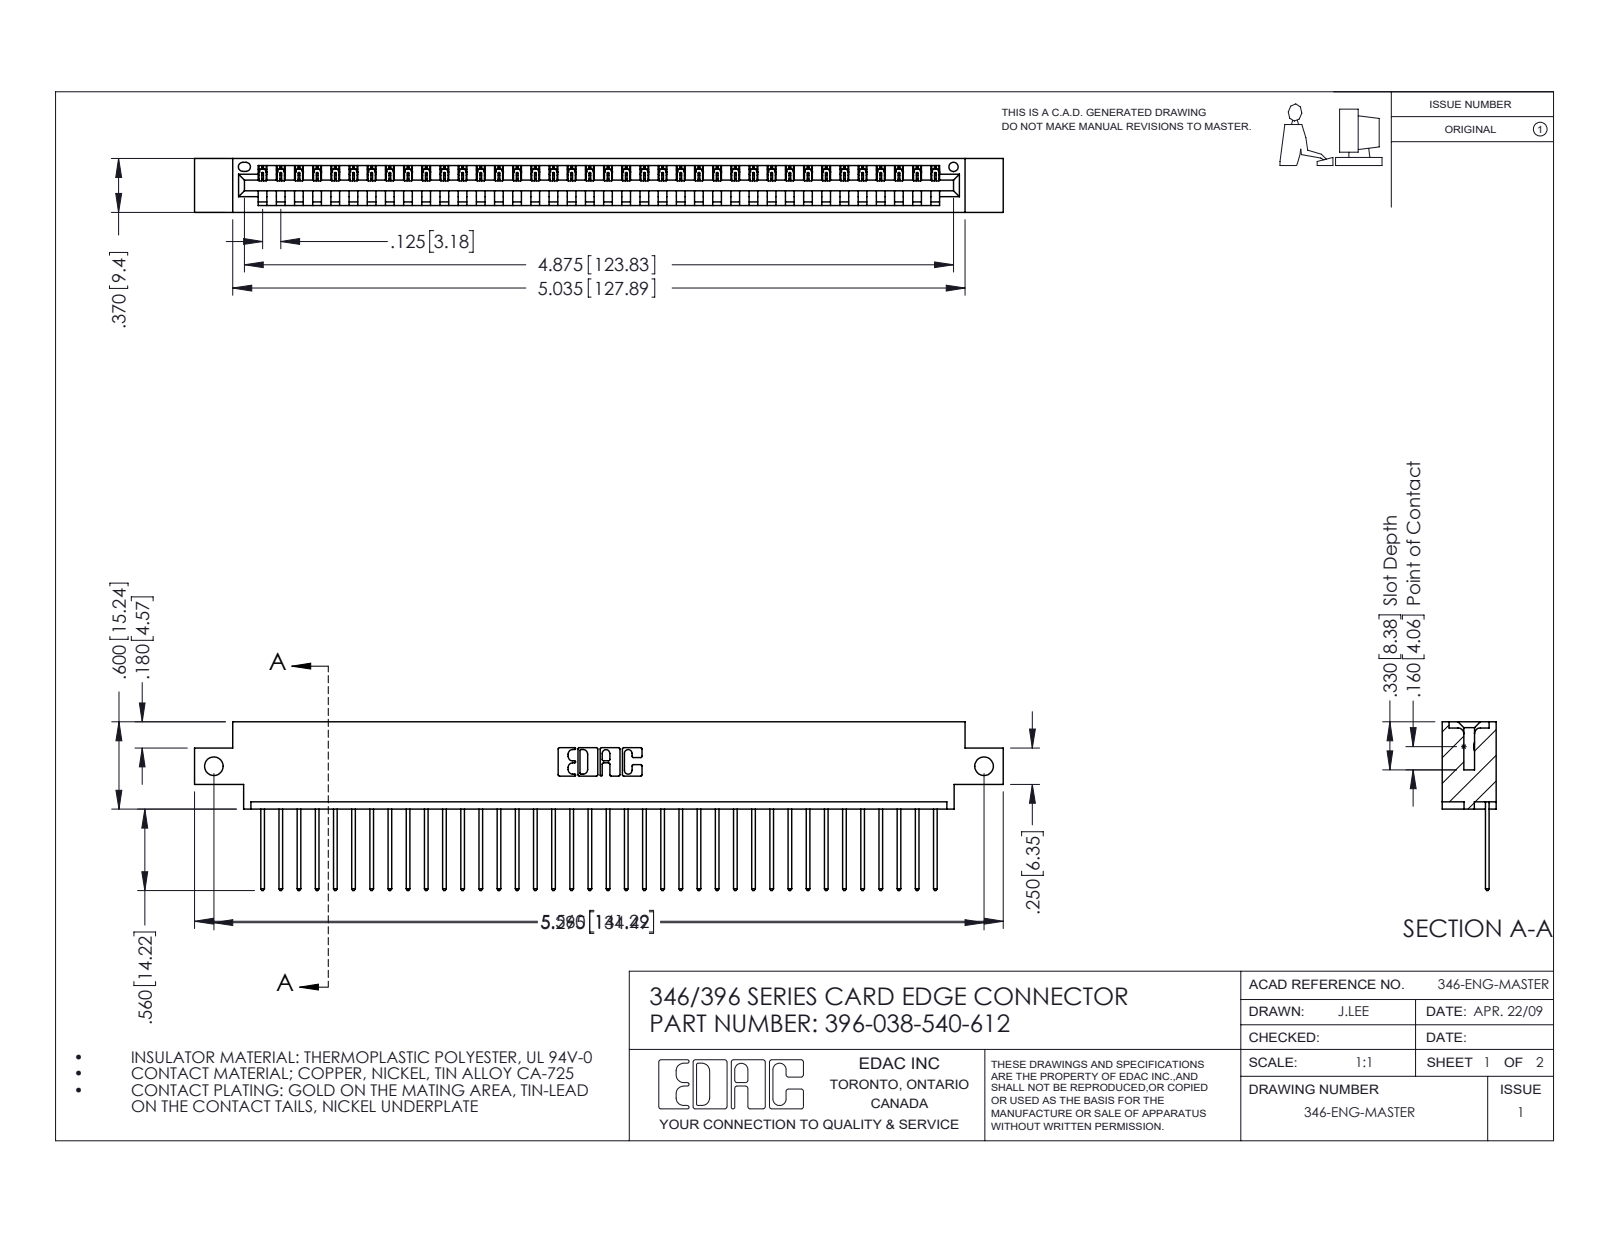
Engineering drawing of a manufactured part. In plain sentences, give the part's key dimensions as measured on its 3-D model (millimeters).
The part is named "396-038-540-612; 346 Part_0.170 Offset - Side Mount; 345-292-001_345-293-140". Its 3-D file was written by "SolidWorks 2016 (CONFIG_CONTROL_DESIGN)". It is 39 solids with 2330 faces: 1600 planar, 730 cylindrical and 0 other. Overall it measures 141.2 by 29.5 by 9.4 millimeters. Its volume is 13 300 cubic millimeters and its surface area 16 970 square millimeters. Round holes: 2 of diameter 3.3, 1 of diameter 1.6. Partial cylindrical surfaces (rounded edges, fillets, slot ends): 76 of radius 0.2, 76 of radius 0.3, 22 of radius 0.3, 6 of radius 0.2, 6 of radius 0.8, 3 of radius 0.7, 2 of radius 0.8, 2 of radius 1. The main face-to-face distances are 1.2, 8.2, 9.4, 6.4, 1.8, 7.6, 0.6, 3.8, 5.6, 2.5. The hole center spacings are 134.5.
